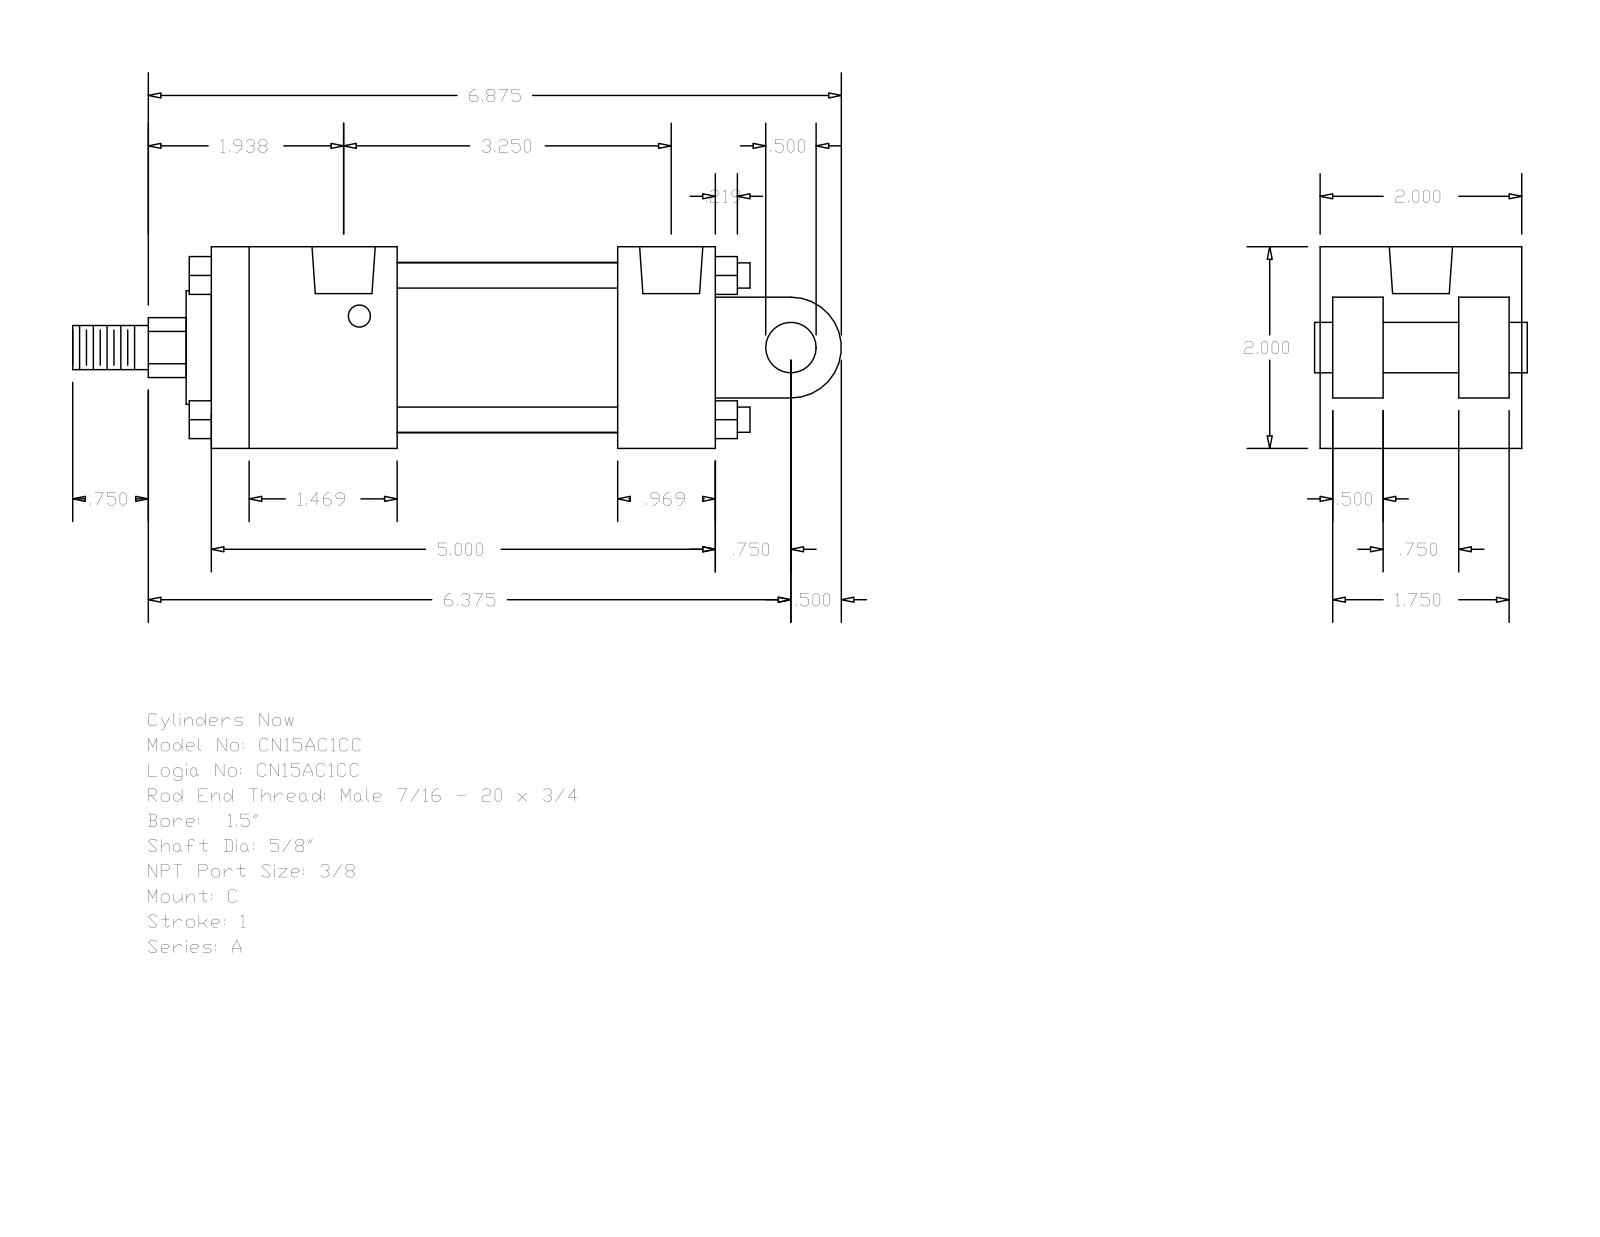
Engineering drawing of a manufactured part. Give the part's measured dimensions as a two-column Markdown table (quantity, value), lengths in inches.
| quantity | value |
| --- | --- |
| part name | A_C__0150_0.625 |
| STEP written by | GSSL Pune (CONFIG_CONTROL_DESIGN) |
| units | inches |
| bodies | 0 solids, 135 faces (102 planar, 33 cylindrical, 0 other) |
| overall size | 7.625 × 2 × 2 |
| round holes (diameter × count) | 0.219 × 4, 0.627 × 2 |
| round bosses / shafts (diameter × count) | 0.25 × 4, 1.69 × 1, 1.125 × 1, 0.625 × 1, 0.5 × 1, 0.437 × 1 |
| partial cylindrical surfaces (radius × count) | 0.297 × 1, 0.5 × 1 |
| main face-to-face distances | 2, 0.5, 5, 1.375, 0.125, 1.875, 0.625, 1.25, 4.031, 0.969 |
| hole center spacings | 0.156, 2.937, 3.094, 3.25 |
